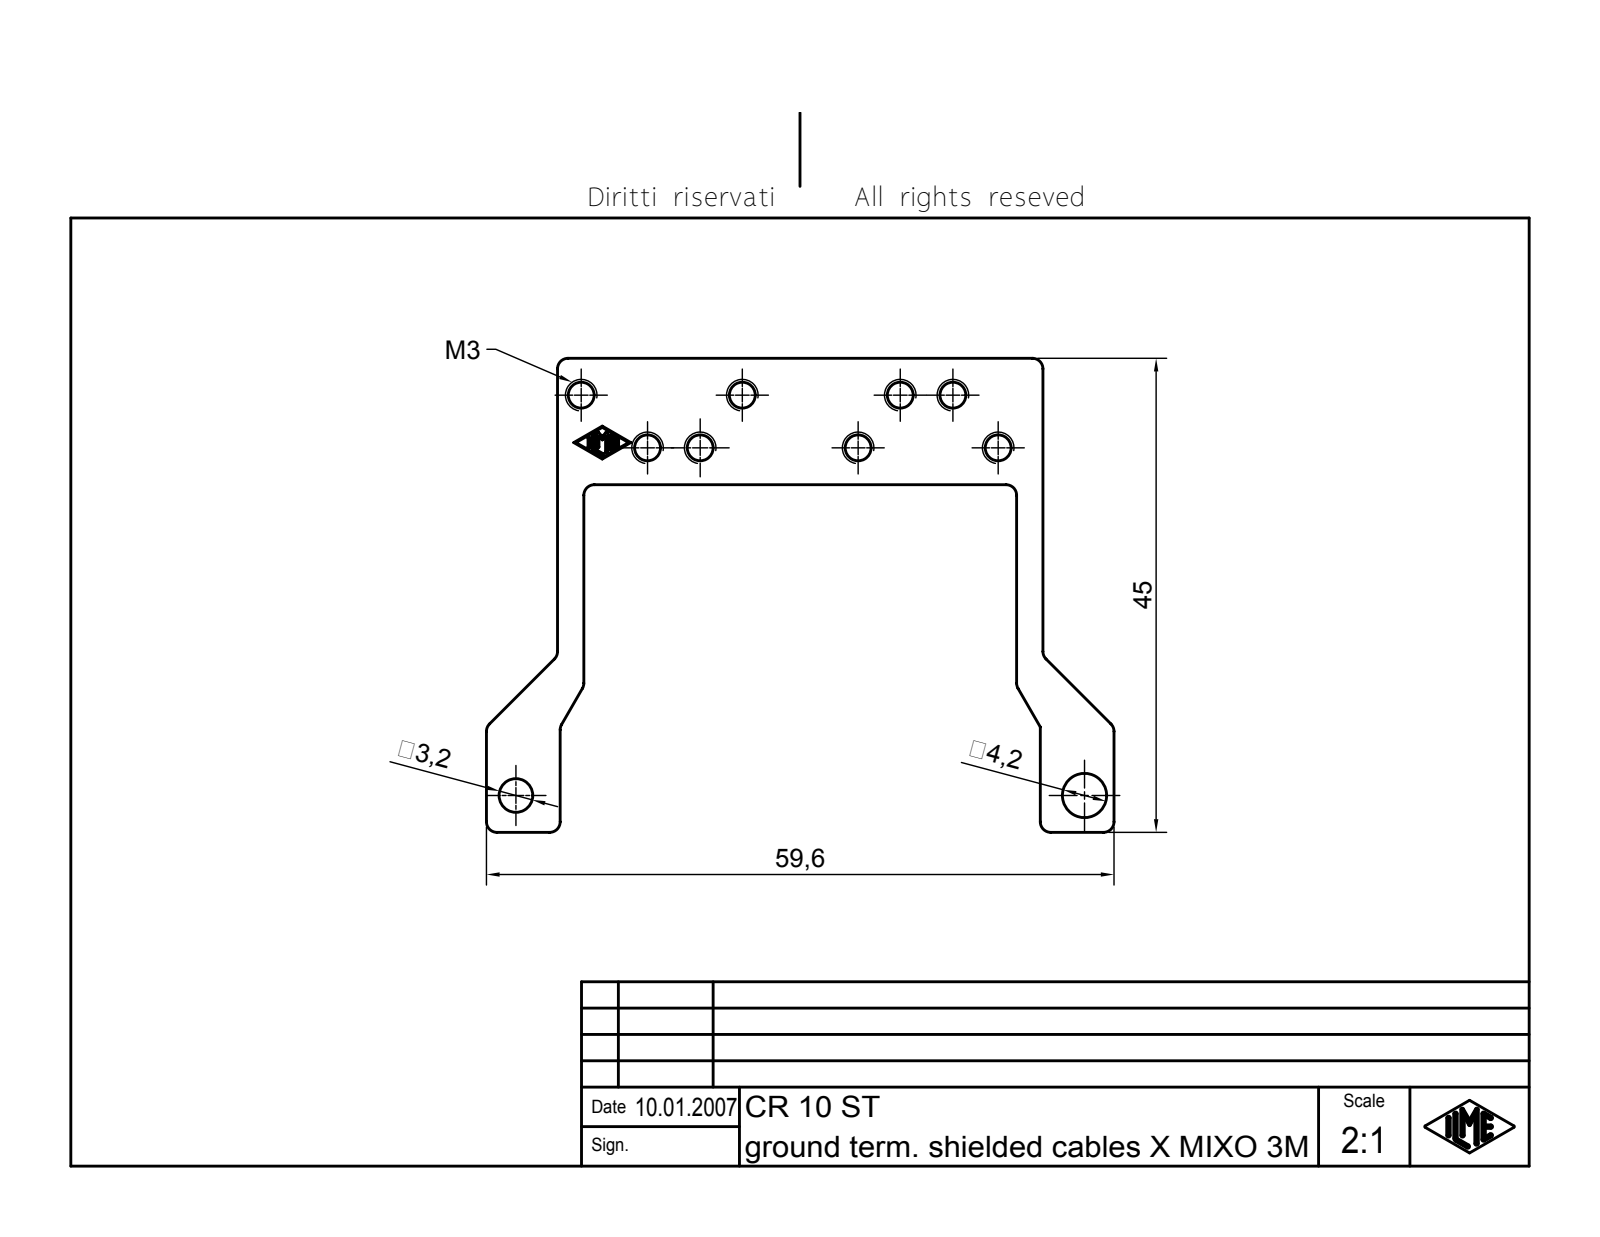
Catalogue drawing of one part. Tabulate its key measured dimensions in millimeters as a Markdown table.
| quantity | value |
| --- | --- |
| part name | CR 10 ST |
| STEP written by | Autodesk Inventor 7 (AUTOMOTIVE_DESIGN) |
| units | millimeters |
| bodies | 1 solid, 119 faces (55 planar, 48 cylindrical, 16 other) |
| overall size | 59.6 × 45 × 2 |
| volume | 1 568 mm³ |
| surface area | 2 269 mm² |
| round holes (diameter × count) | 3.2 × 1, 4.2 × 1 |
| partial cylindrical surfaces (radius × count) | 1 × 15, 0.1 × 14 |
| main face-to-face distances | 2, 12, 2.5, 43.6, 46.1, 41.1, 45.85, 2.25, 43.35, 6.75 |
| hole center spacings | 54 |
